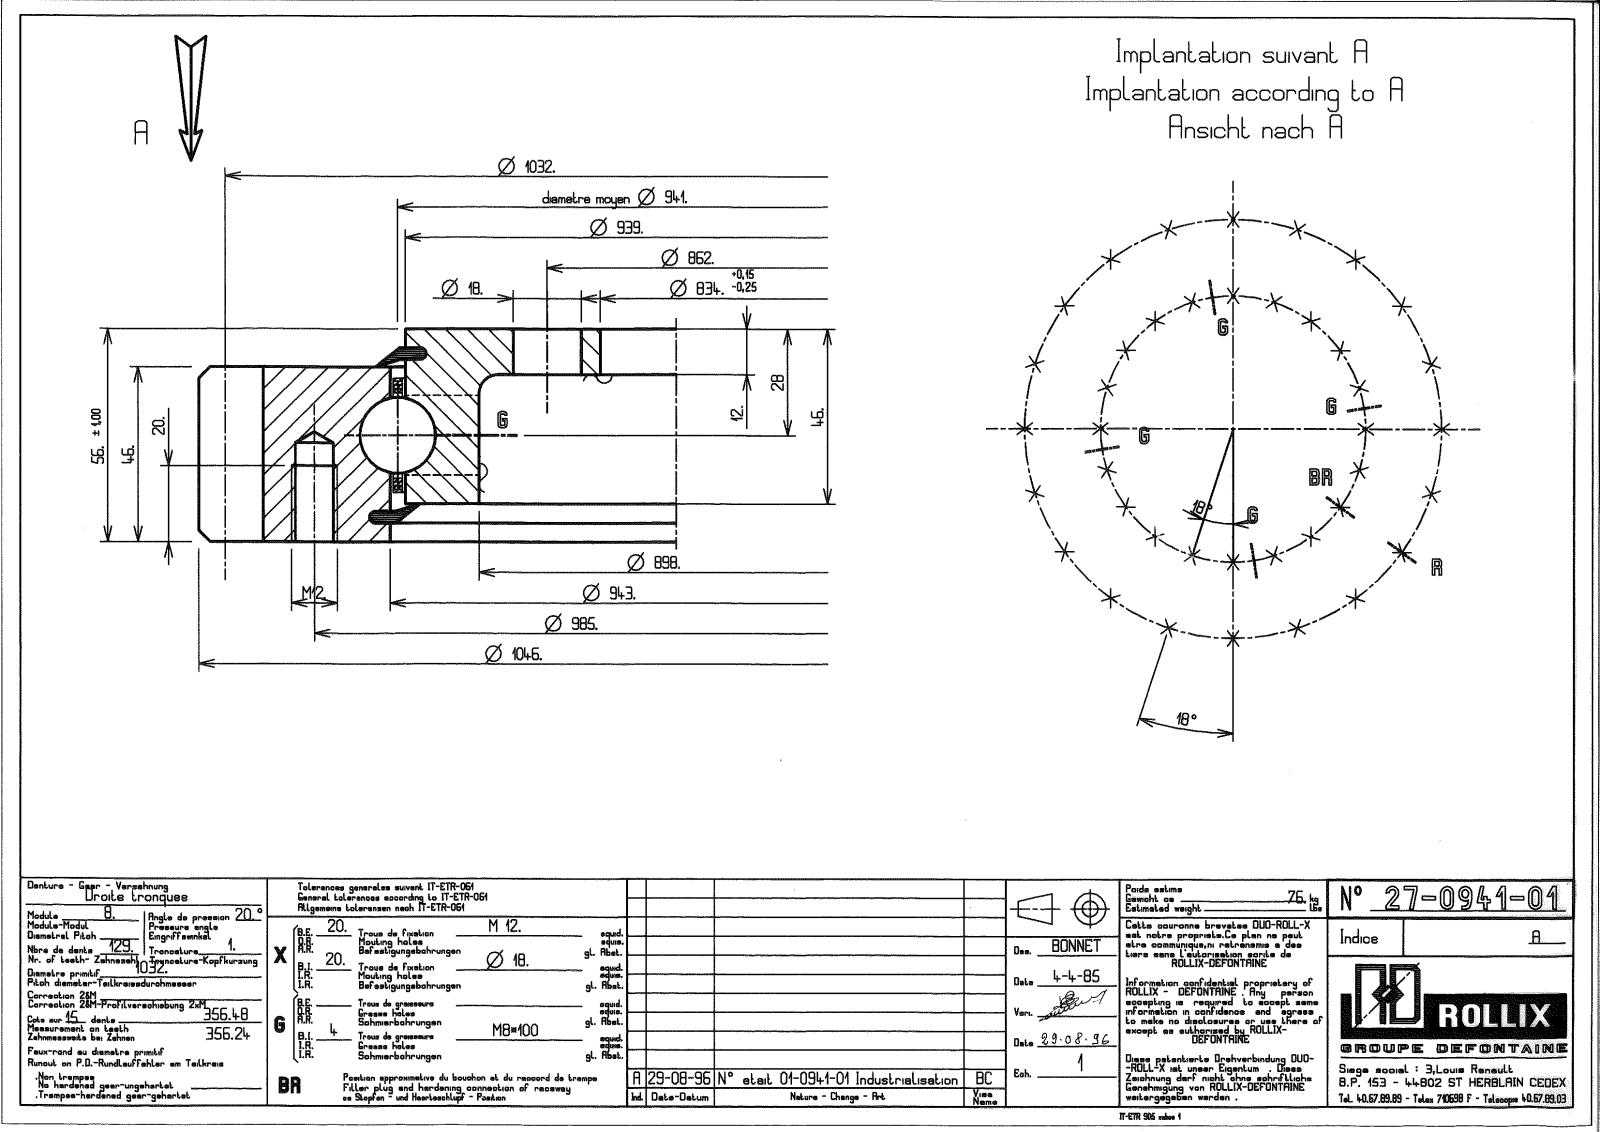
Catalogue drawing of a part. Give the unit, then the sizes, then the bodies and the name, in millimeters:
Units: millimetres
Overall size (bounding box): 1045.99 × 1045.93 × 56
Round holes (diameter × count): ⌀10.25 ×20, ⌀18 ×20, ⌀7 ×2, ⌀834 ×1, ⌀898 ×1, ⌀945.5 ×1
Round bosses / shafts (diameter × count): ⌀8 ×2, ⌀936.5 ×1
Partial cylindrical surfaces — rounded edges, fillets, slot ends (radius × count): R506 ×1, R523 ×1
Main face-to-face distances: 10, 46, 56, 44, 2, 12, 34, 36, 8.05, 47.95
Hole centre spacings: 154.09, 492.5, 796.88, 291.31, 422.83, 545.1, 447.18, 578.97
Volume: 9 038 000 mm³ · Surface area: 1 524 000 mm²
Bodies: 9 solids, 1051 faces (311 planar, 371 cylindrical, 369 other)
Part name (STEP PRODUCT): 21-0941-01
STEP written by: SolidWorks 2016 (CONFIG_CONTROL_DESIGN)
